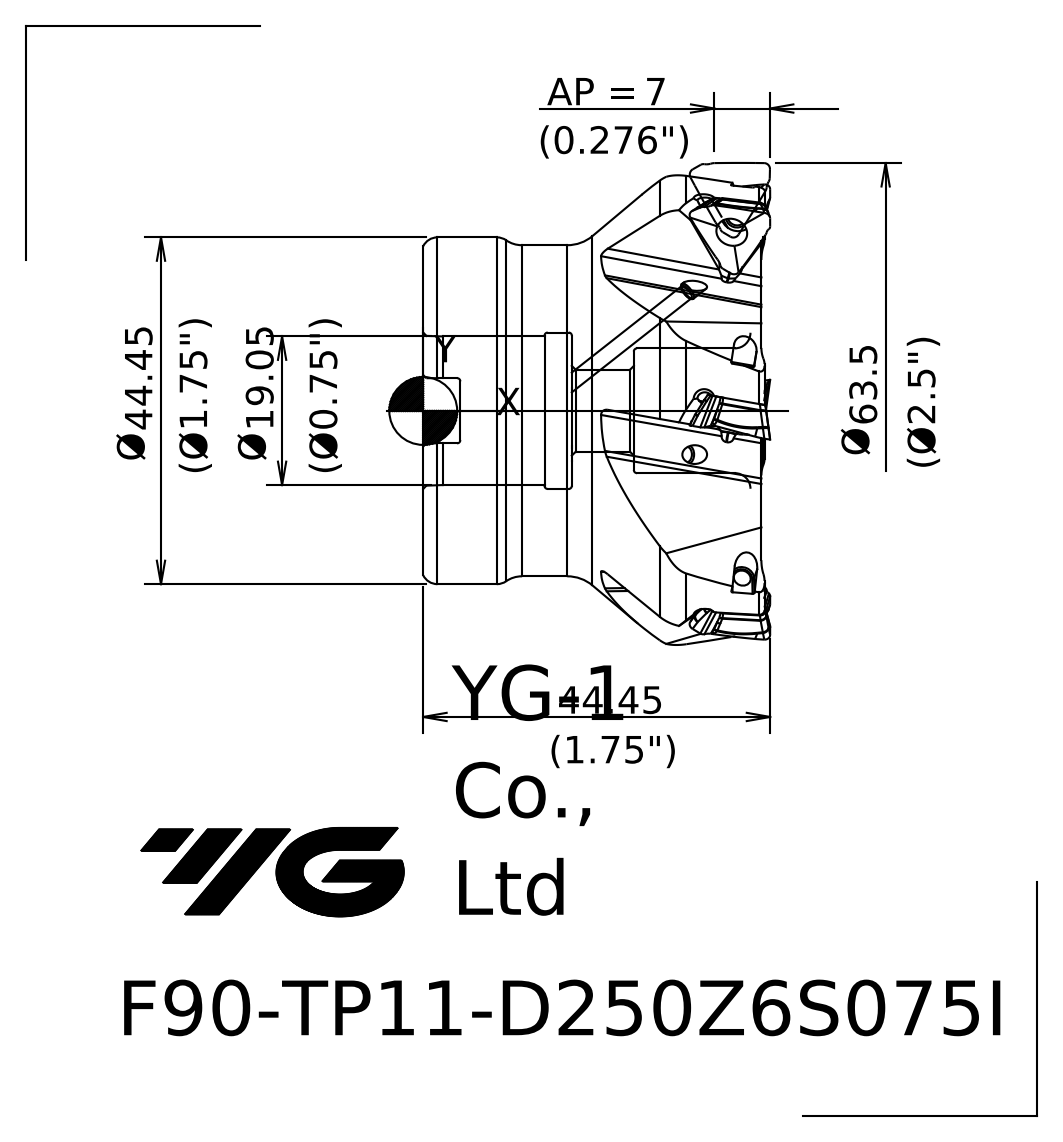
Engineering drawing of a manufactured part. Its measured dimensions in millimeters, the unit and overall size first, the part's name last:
Units: millimetres
Overall size (bounding box): 63.54 × 63.54 × 44.45
Round holes (diameter × count): ⌀10.5 ×1, ⌀16 ×1, ⌀19.05 ×1, ⌀20.05 ×1
Round bosses / shafts (diameter × count): ⌀44.45 ×1, ⌀42.45 ×1
Partial cylindrical surfaces — rounded edges, fillets, slot ends (radius × count): R0.4 ×2
Main face-to-face distances: 43.35, 1.4, 41.95, 38.6, 37.2, 4.75, 24.3, 22.9, 14.3, 19.05
Volume: 77 546 mm³ · Surface area: 19 467 mm²
Bodies: 1 solid, 76 faces (18 planar, 10 cylindrical, 48 other)
Part name (STEP PRODUCT): 1022A408ED39nsfa
STEP written by: SIEMENS PLM Software NX 10.0 (AP203_CONFIGURATION_CONTROLLED_3D_DESIGN_OF_MECHANICAL_PARTS_AND_ASSEMBLIES_MIM_LF)
